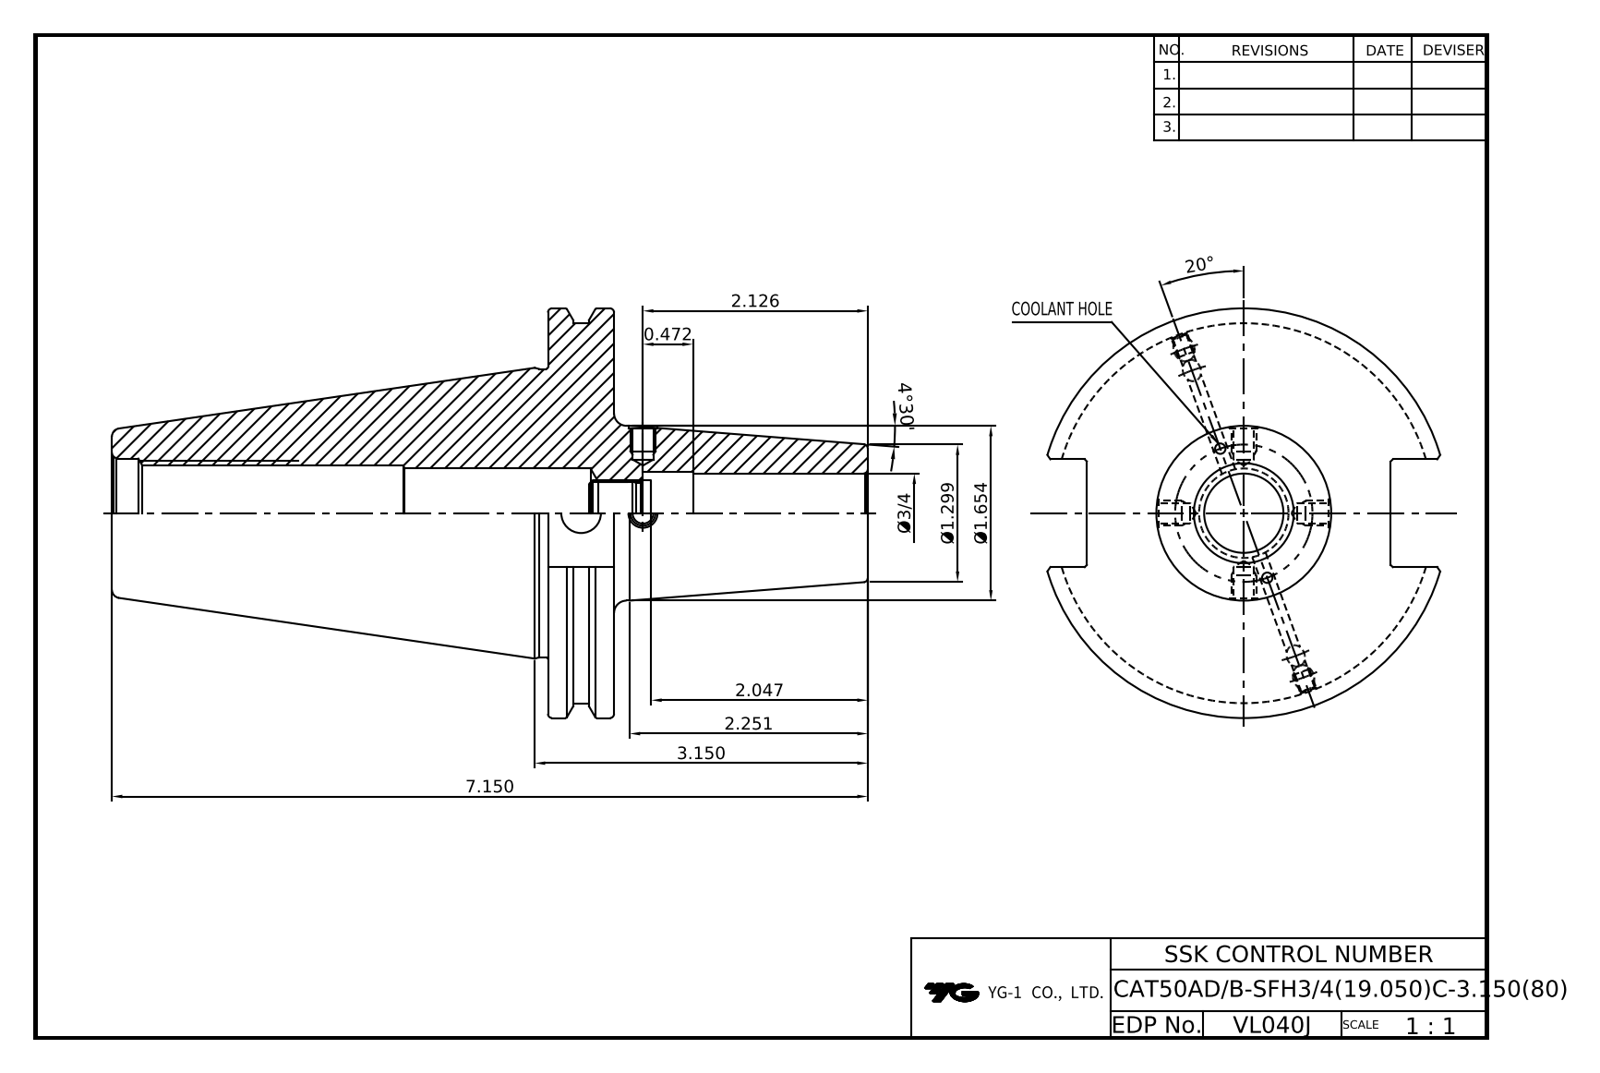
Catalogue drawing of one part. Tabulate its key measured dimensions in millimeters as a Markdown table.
| quantity | value |
| --- | --- |
| part name | LO-CAT50ADB-SFH19.05C-80 |
| STEP written by | Autodesk Inventor 2024 (AUTOMOTIVE_DESIGN) |
| units | millimeters |
| bodies | 1 solid, 90 faces (39 planar, 29 cylindrical, 22 other) |
| overall size | 181.6 × 98.42 × 94.69 |
| volume | 371 146 mm³ |
| surface area | 55 743 mm² |
| round holes (diameter × count) | 2.5 × 2, 3.24 × 2, 4.13 × 2, 4.2 × 2, 5 × 2, 9.53 × 1, 14.92 × 1, 19.05 × 1, 19.65 × 1, 21.5 × 1, 21.97 × 1, 26.2 × 1 |
| round bosses / shafts (diameter × count) | 98.42 × 1, 91.29 × 1, 69.25 × 1, 42 × 1 |
| main face-to-face distances | 15.88, 104.77, 120.65, 181.6, 76.83, 60.95, 73.03, 25.9, 110.82, 6.05 |
